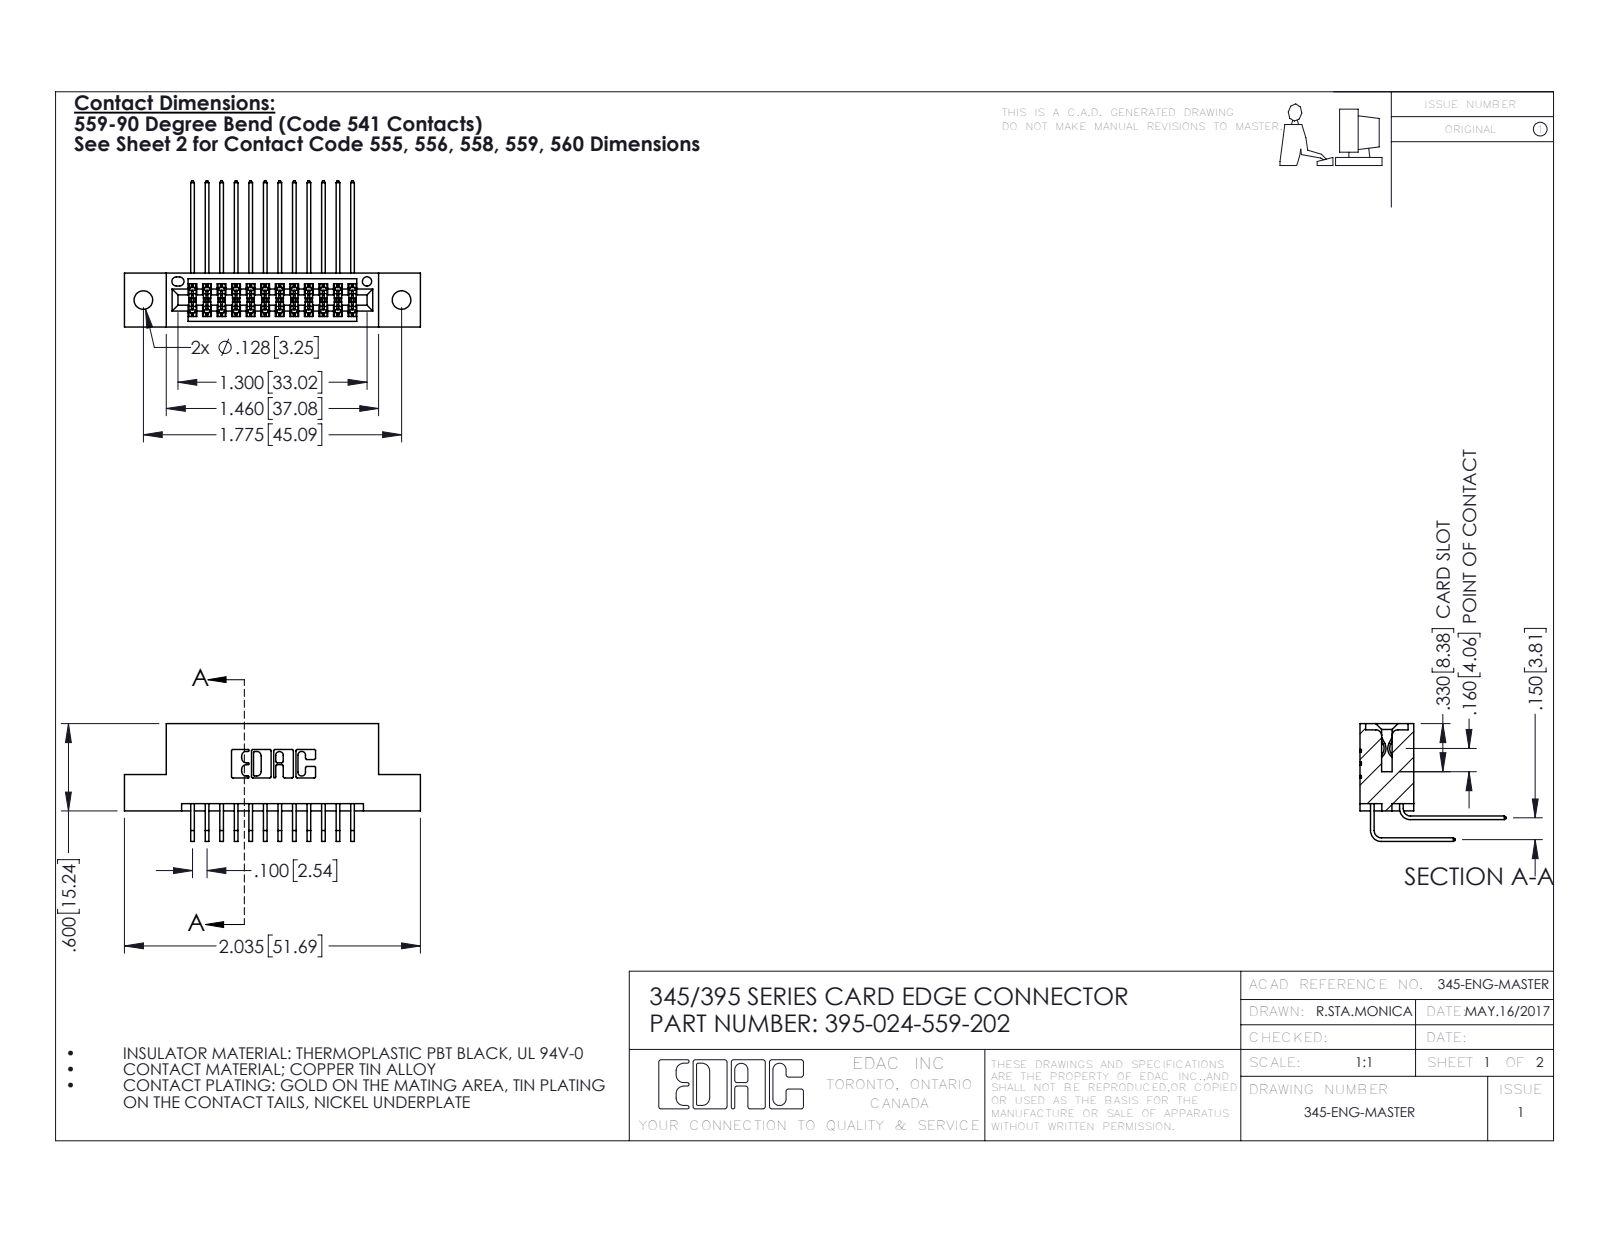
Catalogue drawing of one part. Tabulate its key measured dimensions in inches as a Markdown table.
| quantity | value |
| --- | --- |
| part name | 345-292-001_559 Tail - 2; 395-024-559-202; 345-292-001_558 559 Tail - 1; 345 Part_Flush Mounting Lugs - 0.128 Dia |
| STEP written by | SolidWorks 2016 (CONFIG_CONTROL_DESIGN) |
| units | inches |
| bodies | 25 solids, 1374 faces (920 planar, 454 cylindrical, 0 other) |
| overall size | 2.035 × 1.005 × 0.809 |
| volume | 0.296 in³ |
| surface area | 10.79 in² |
| round holes (diameter × count) | 0.128 × 2, 0.064 × 1 |
| partial cylindrical surfaces (radius × count) | 0.006 × 36, 0.01 × 22, 0.007 × 6, 0.031 × 6, 0.026 × 3, 0.014 × 2, 0.019 × 2, 0.022 × 2 |
| main face-to-face distances | 0.2, 0.072, 0.298, 0.37, 0.098, 0.272, 0.025, 0.225, 0.15, 0.1 |
| hole center spacings | 0.27, 1.543, 1.775 |
